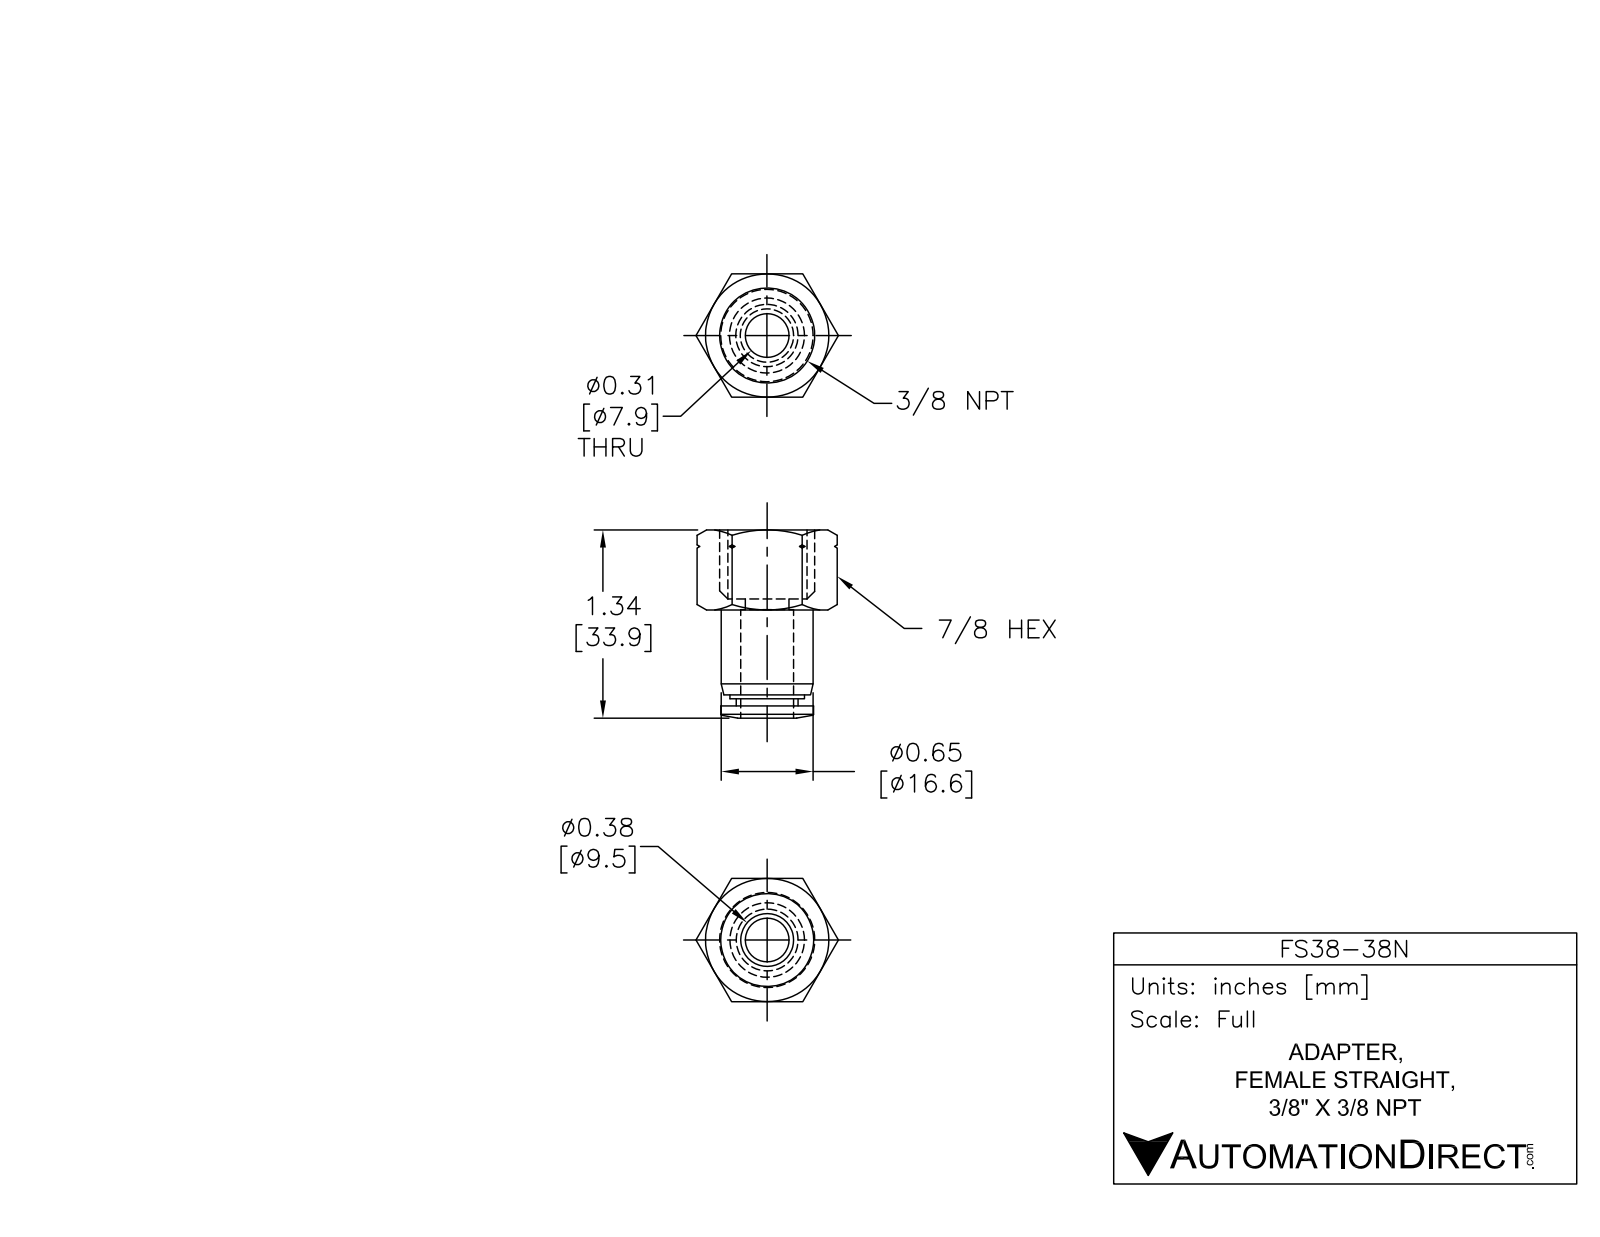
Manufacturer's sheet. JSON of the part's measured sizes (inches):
{"part_name": "FS38-38N", "step_written_by": "SolidWorks 2015 (AUTOMOTIVE_DESIGN)", "units": "inches", "bodies": {"solids": 1, "faces": 65, "planar": 13, "cylindrical": 12, "other": 40}, "overall_size": [1.343, 1, 0.866], "volume_in3": 0.349, "surface_area_in2": 6.634, "round_holes": [[0.315, 1], [0.386, 1]], "round_bosses_or_shafts": [[0.661, 1], [0.656, 1], [0.531, 1], [0.441, 1]], "face_to_face_distances": [0.866, 0.079, 0.685, 0.492, 0.571, 1.256, 0.764, 1.177, 0.606, 1.205]}
